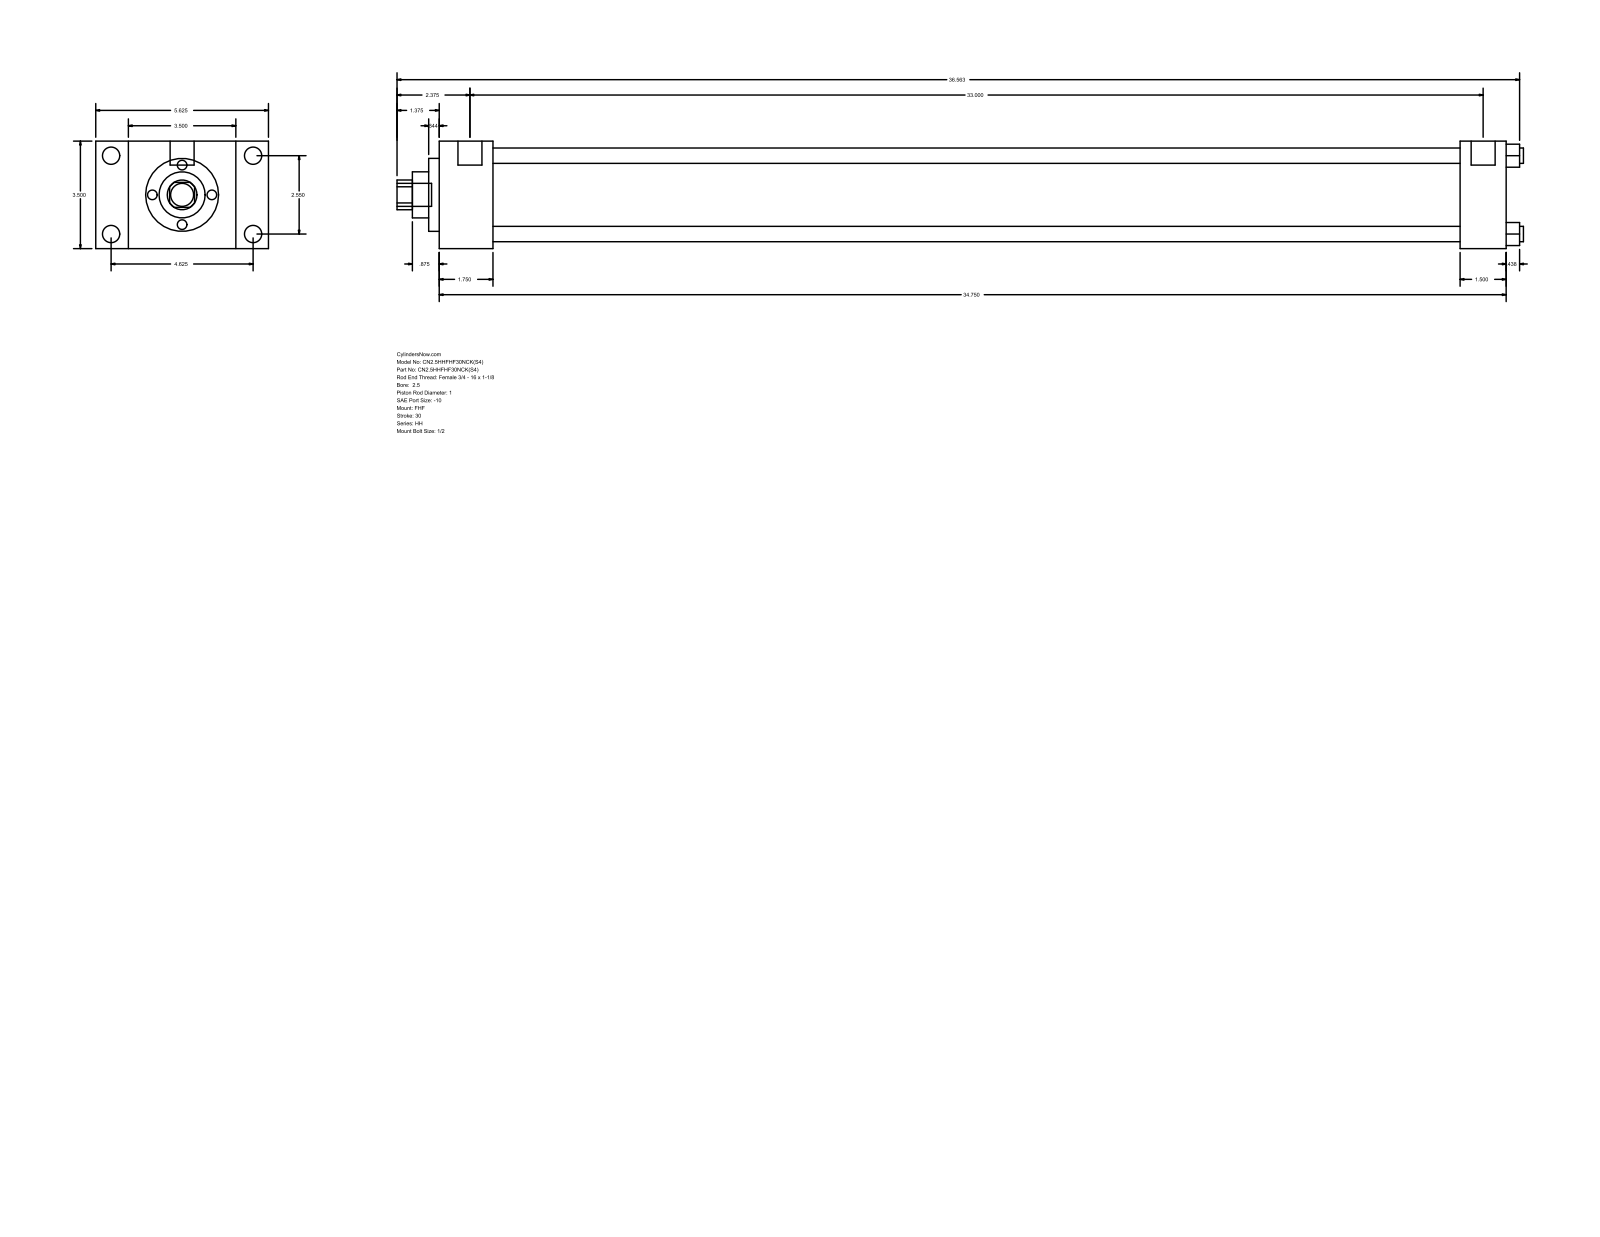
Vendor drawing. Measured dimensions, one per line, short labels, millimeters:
name: HH_FHF__0250_1
written by: GSSL Pune (CONFIG_CONTROL_DESIGN)
unit: mm
bodies: 0 solids, 90 faces (61 planar, 29 cylindrical, 0 other)
size: 931.86 × 142.88 × 88.9
holes: 4× ⌀12.7, 1× ⌀25.4, 1× ⌀38.1, 1× ⌀60.33, 1× ⌀73.03
bosses: 4× ⌀14.3, 4× ⌀5.56, 2× ⌀19.84, 1× ⌀19.05
rounds: 1× R12.29
face distances: 88.9, 44.46, 26.99, 115.89, 882.66, 838.2, 142.88, 844.56, 800.1, 38.1
hole spacings: 45.79, 64.76, 91.58
